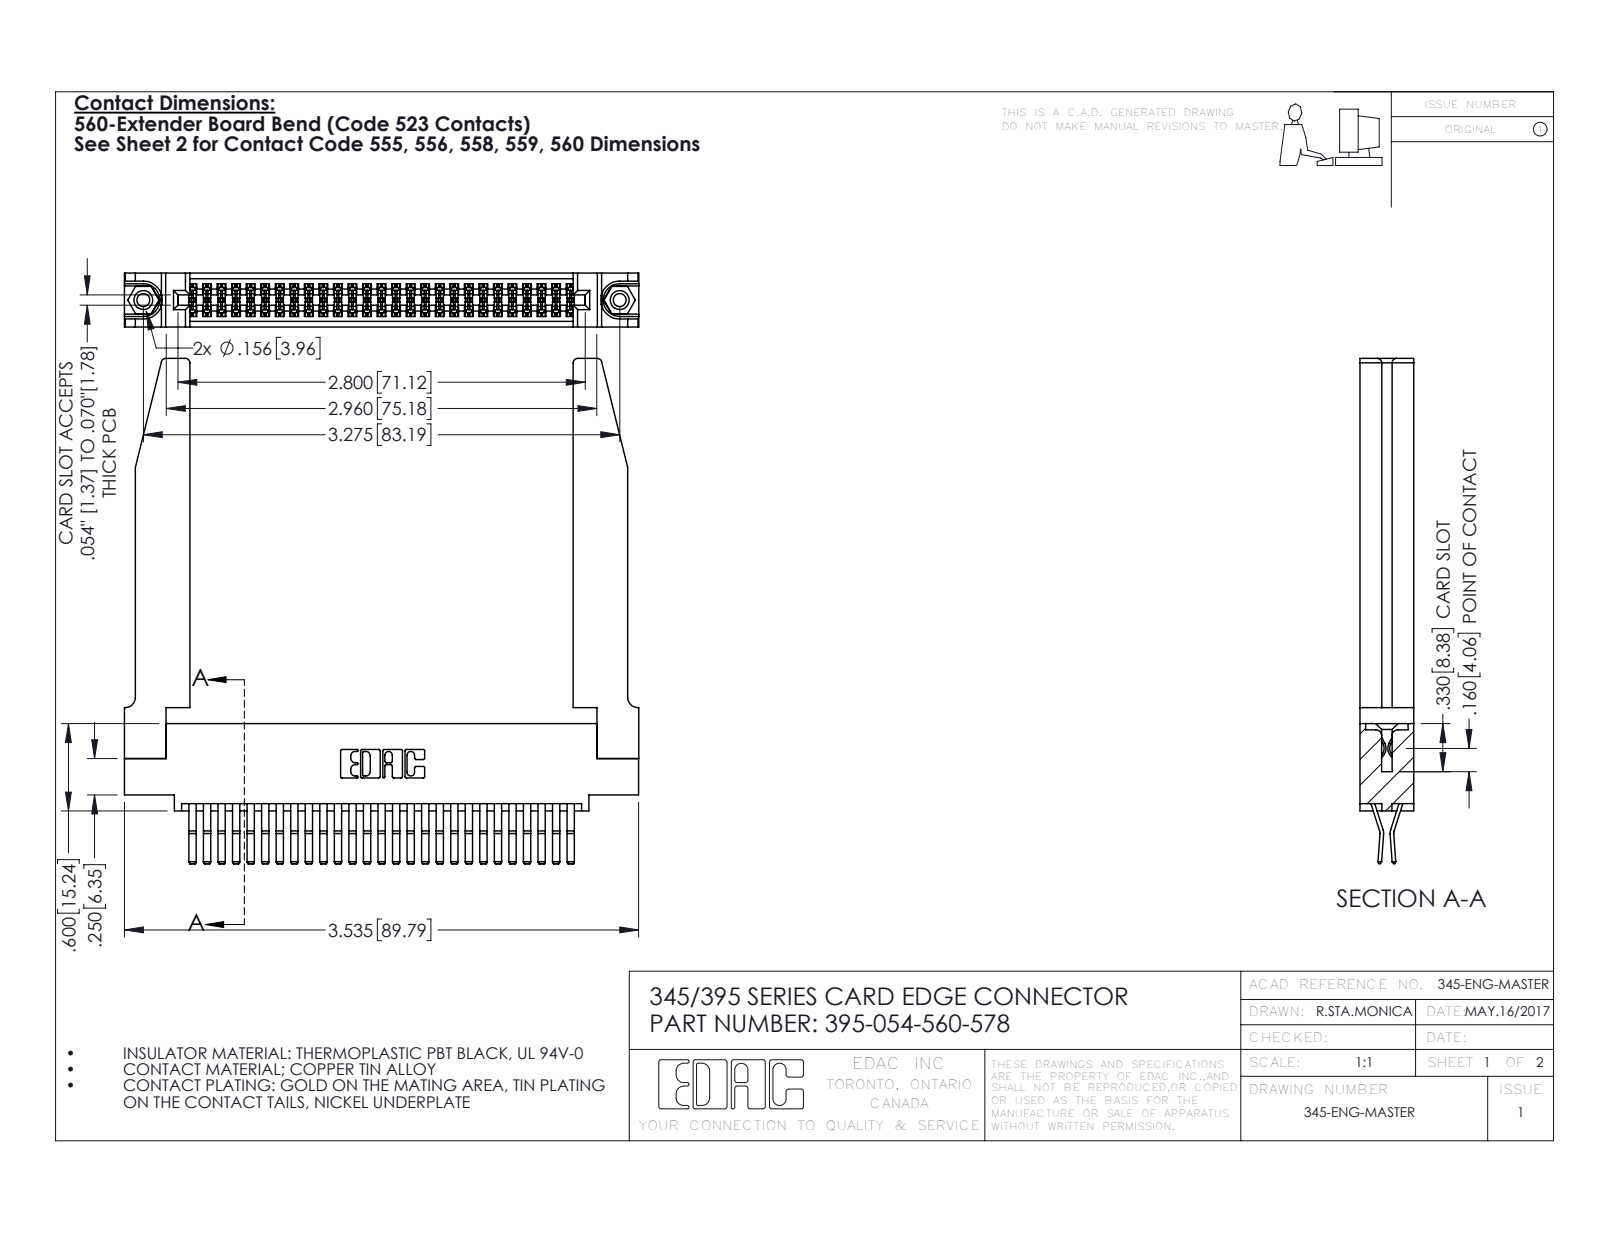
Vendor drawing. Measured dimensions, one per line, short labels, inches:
name: 395-054-560-578; 345-250-001_345-250-001-102; 345 Part_0.110 Offset - 0.156 Dia-TH; 345-220-078_345-220-078 (+1 more)
written by: SolidWorks 2016 (CONFIG_CONTROL_DESIGN)
unit: in
bodies: 59 solids, 3172 faces (2008 planar, 1112 cylindrical, 52 other)
size: 3.536 × 3.472 × 0.37
volume: 1.015 in³; area: 32.02 in²
holes: 2× ⌀0.089, 2× ⌀0.125, 2× ⌀0.156, 1× ⌀0.064
bosses: 2× ⌀0.155
rounds: 81× R0.006, 22× R0.01, 8× R0.03, 6× R0.007, 6× R0.031, 3× R0.026, 2× R0.01, 2× R0.014
face distances: 0.37, 0.072, 0.298, 0.025, 0.2, 0.098, 0.272, 0.225, 0.148, 0.15
hole spacings: 0.27, 3.04, 3.275
